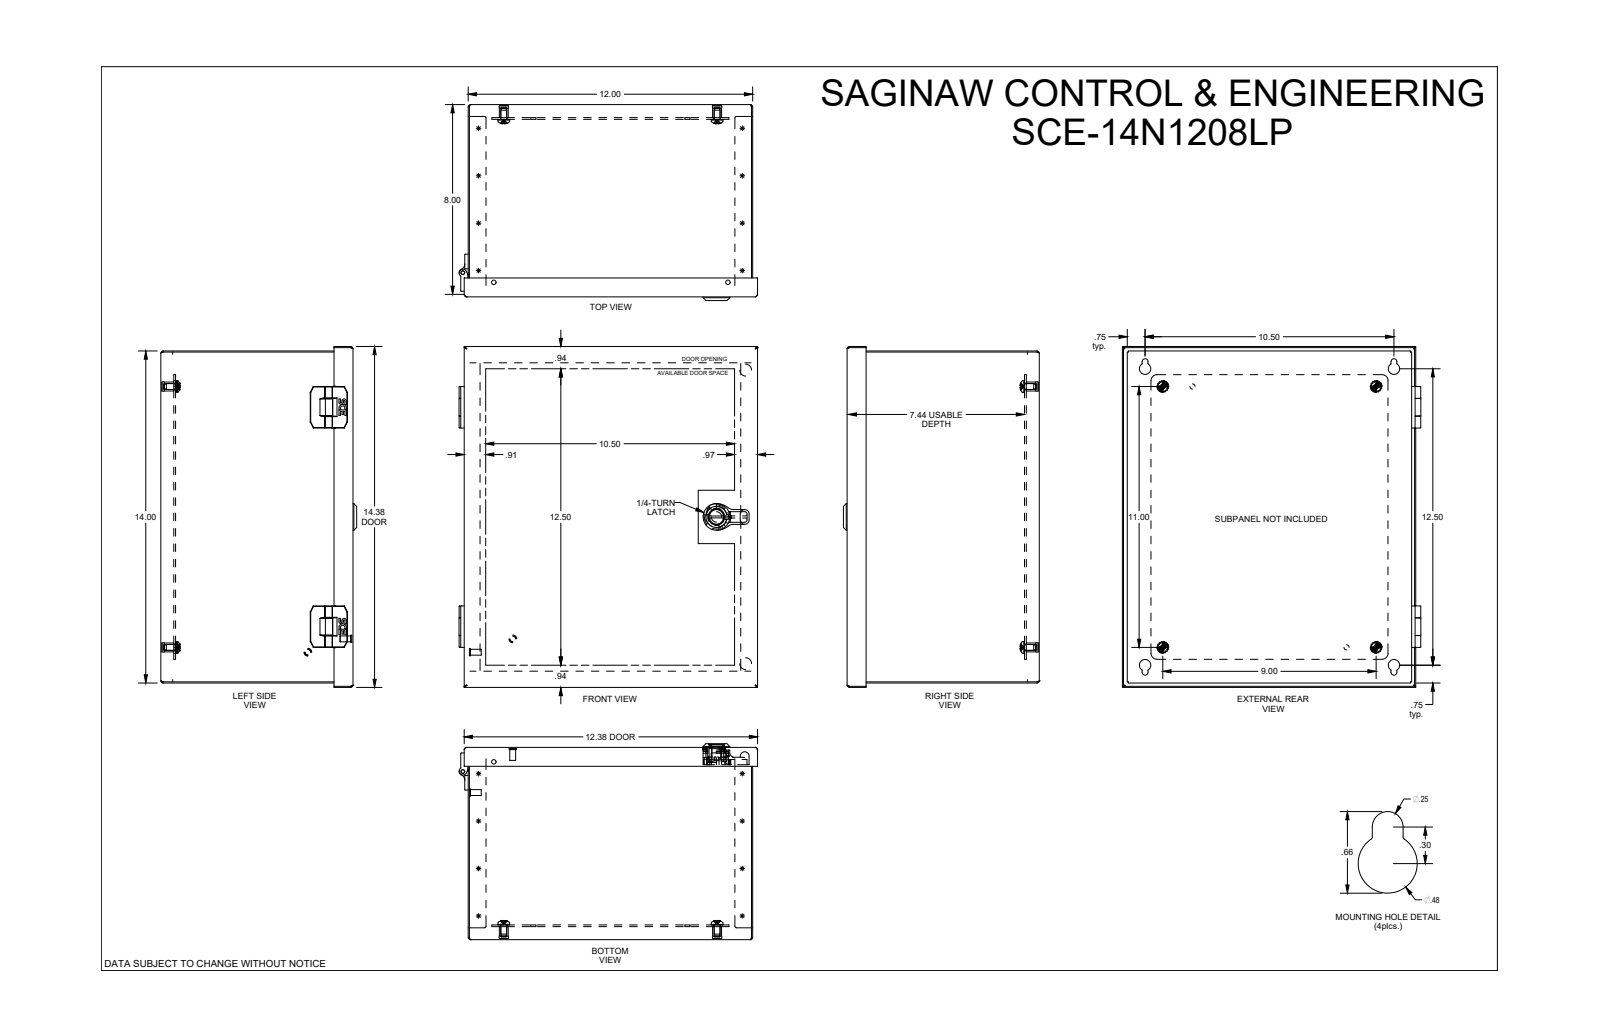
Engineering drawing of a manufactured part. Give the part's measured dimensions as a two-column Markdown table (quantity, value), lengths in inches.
| quantity | value |
| --- | --- |
| part name | SCE-14N1208LP |
| STEP written by | SolidWorks 2019 (AUTOMOTIVE_DESIGN) |
| units | inches |
| bodies | 31 solids, 1529 faces (554 planar, 645 cylindrical, 330 other) |
| overall size | 14.383 × 12.593 × 8.263 |
| volume | 59.89 in³ |
| surface area | 1 926 in² |
| round holes (diameter × count) | 0.17 × 4, 0.203 × 4, 0.25 × 4, 0.281 × 4, 0.329 × 4, 0.343 × 4, 0.48 × 4, 0.193 × 3, 0.187 × 2, 0.218 × 2, 0.158 × 1, 0.44 × 1 |
| round bosses / shafts (diameter × count) | 0.248 × 6, 0.492 × 4, 0.479 × 4, 0.376 × 4, 0.237 × 4, 0.16 × 4, 0.5 × 2, 0.323 × 2 |
| partial cylindrical surfaces (radius × count) | 0.01 × 253, 0.02 × 95, 0.06 × 25, 0.015 × 24, 0.025 × 24, 0.055 × 6, 0.25 × 6, 0.125 × 4 |
| main face-to-face distances | 0.06, 8.047, 11.94, 13.94, 7.987, 8.107, 0.623, 0.563, 7.424, 7.484 |
| hole center spacings | 1.061, 7.75, 9.779, 11.774, 15.269, 1.089, 1.091, 9.25 |
